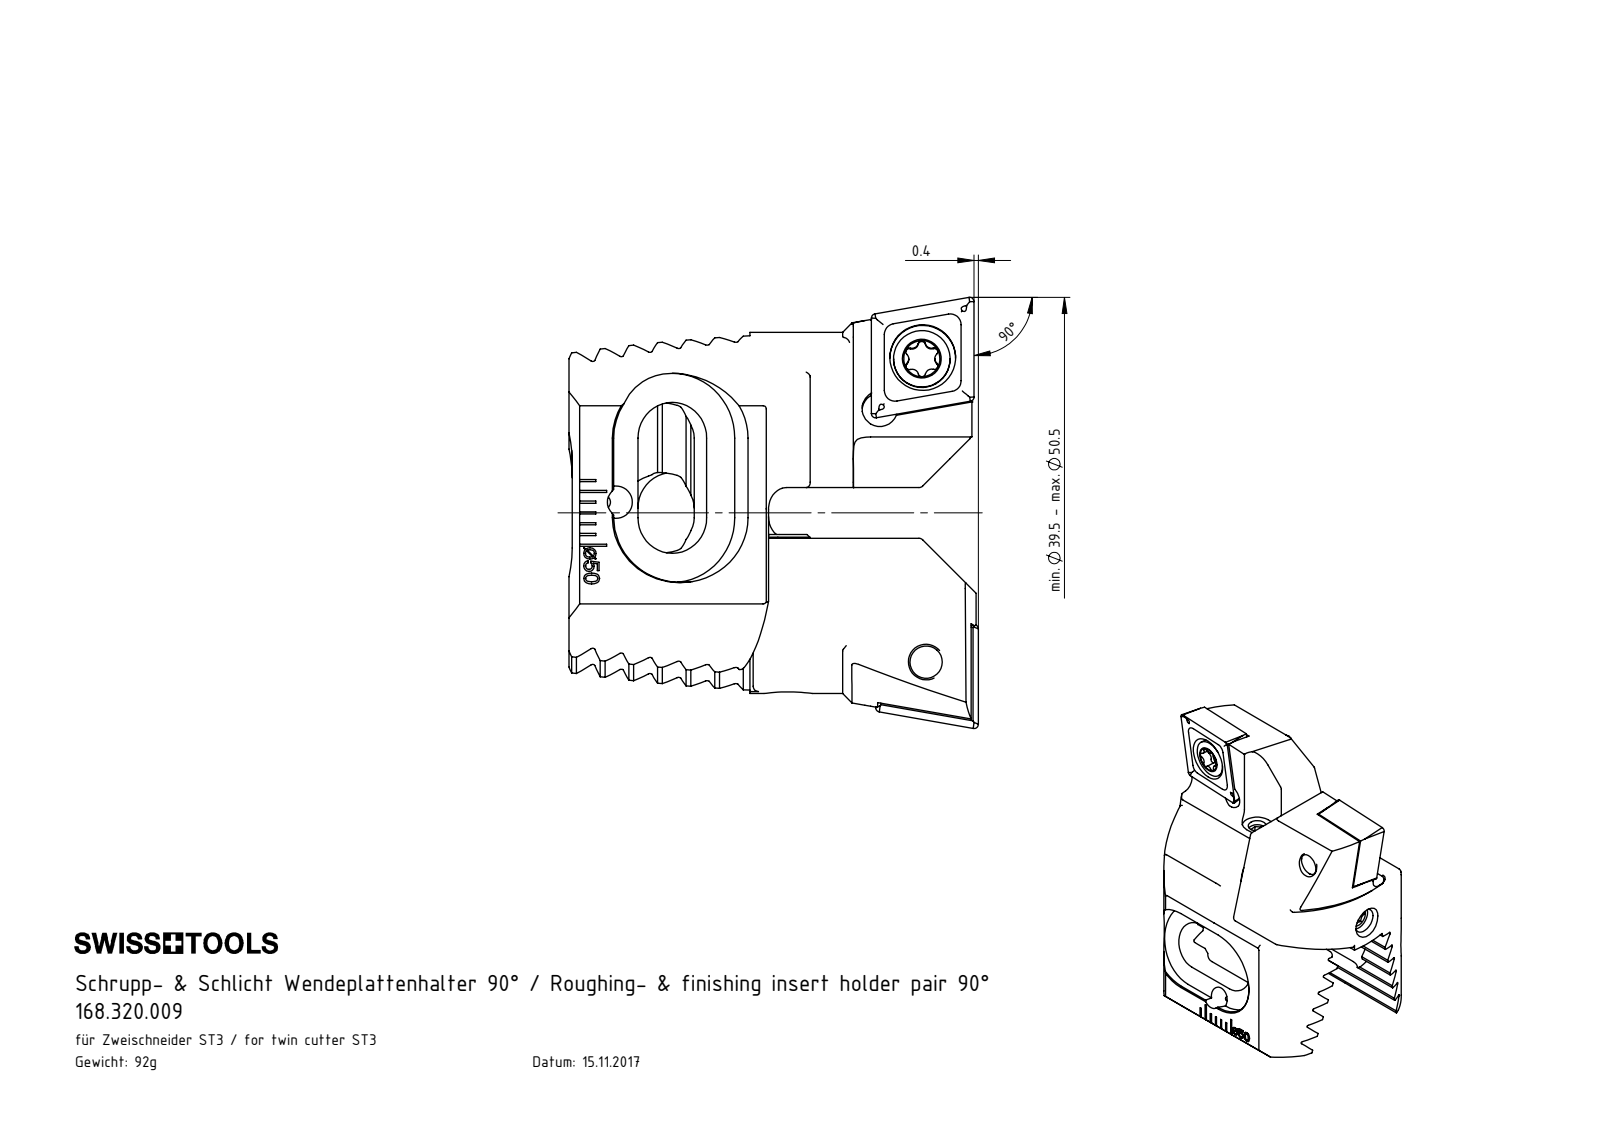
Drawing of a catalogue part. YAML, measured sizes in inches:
part_name: "ZC3-xxx.001.021_A_versetzt Combi; CCMT09T304; ISO 4028 - M3 x 5_M3x8; Z32-ER3.001.013_A (+3 more)"
step_written_by: "SolidWorks 2017 (CONFIG_CONTROL_DESIGN)"
units: inches
bodies: {solids: 9, faces: 683, planar: 326, cylindrical: 143, other: 214}
overall_size: [1.575, 1.496, 1.031]
volume: 0.723
surface_area: 12.85
round_holes:
  - {diameter: 0.13, count: 4}
  - {diameter: 0.079, count: 2}
  - {diameter: 0.173, count: 2}
  - {diameter: 0.24, count: 2}
  - {diameter: 0.063, count: 1}
  - {diameter: 0.098, count: 1}
  - {diameter: 0.118, count: 1}
  - {diameter: 0.138, count: 1}
round_bosses_or_shafts:
  - {diameter: 0.157, count: 4}
  - {diameter: 0.207, count: 2}
  - {diameter: 0.118, count: 1}
  - {diameter: 0.079, count: 1}
partial_cylinders:
  - {radius: 0.02, count: 16}
  - {radius: 0.008, count: 12}
  - {radius: 0.013, count: 12}
  - {radius: 0.023, count: 12}
  - {radius: 0.079, count: 4}
  - {radius: 0.13, count: 4}
  - {radius: 0.236, count: 4}
  - {radius: 0.472, count: 4}
face_to_face_distances: [0.094, 0.187, 0.375, 0.281, 0.193, 0.469, 0.281, 0.05, 0.188, 0.016]
hole_center_spacings: [0.239, 0.244, 1.128, 0.016, 0.354, 0.359, 0.759, 0.952]
